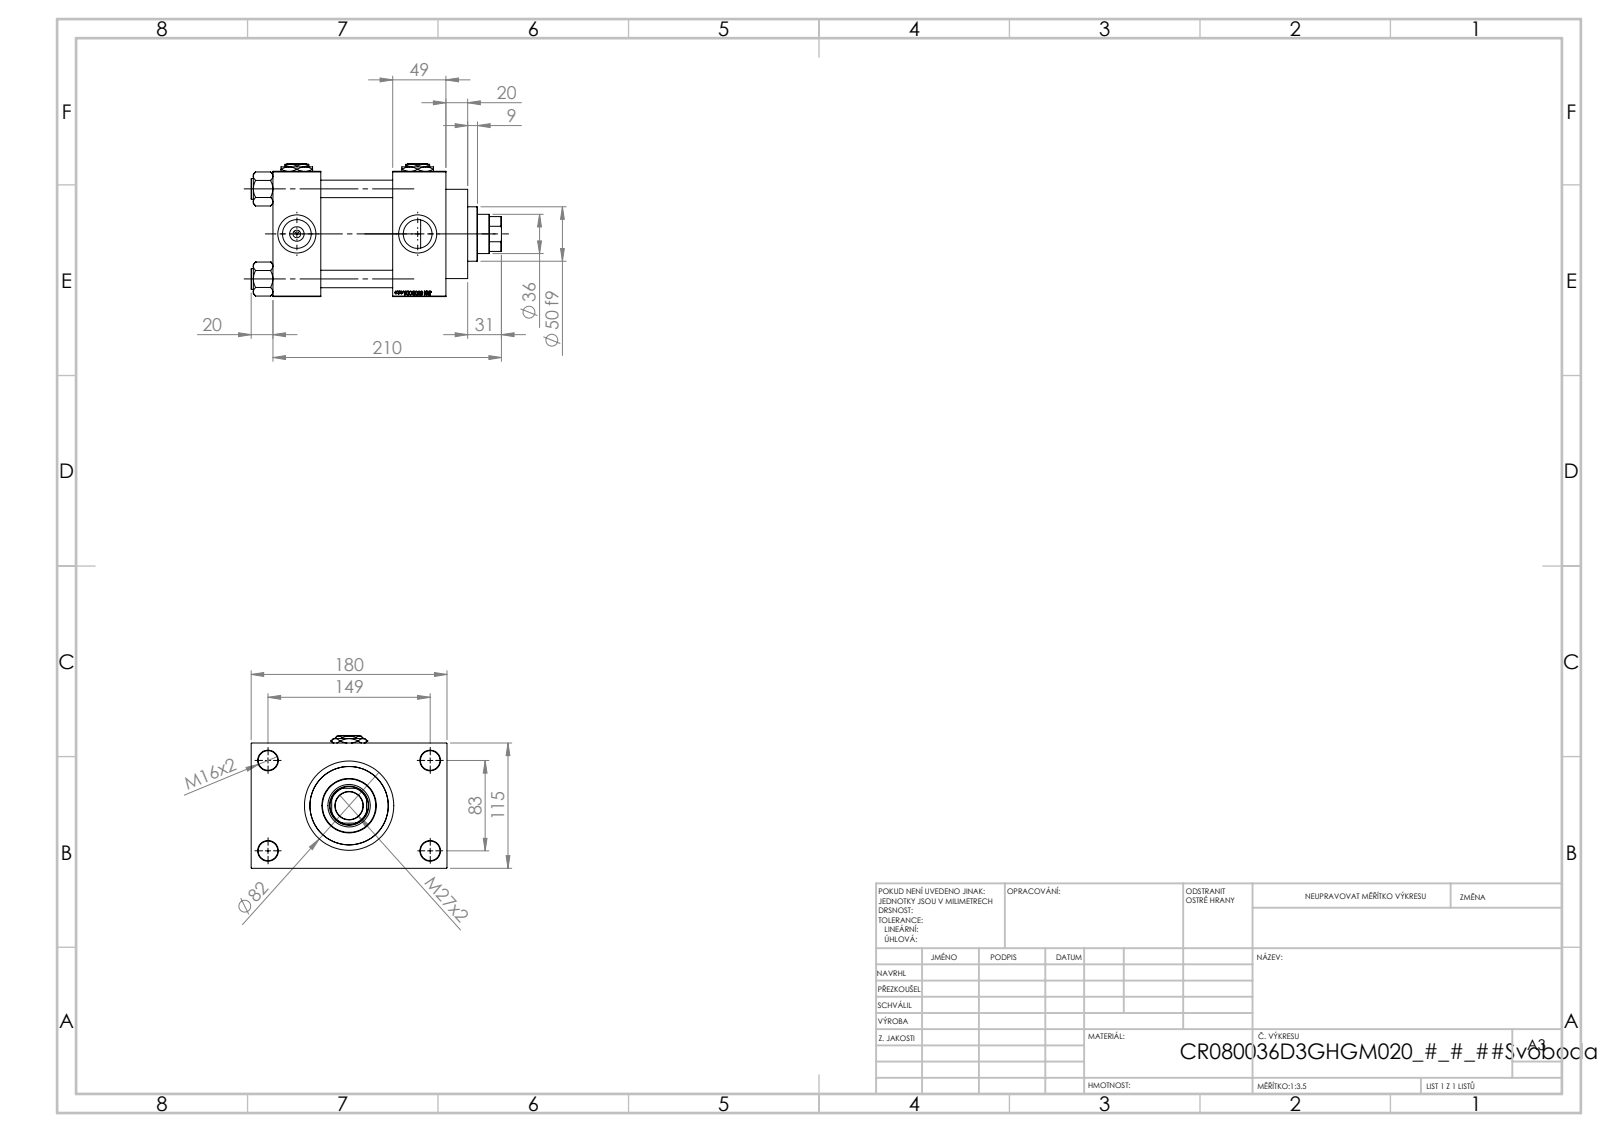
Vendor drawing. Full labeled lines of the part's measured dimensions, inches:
Part name (STEP PRODUCT): V215CR_VCP_D; NUT_M5_D; V215_VC_A; V215CR_D_Body (+2 more)
STEP written by: SolidWorks 2019 (CONFIG_CONTROL_DESIGN)
Units: inches
Bodies: 13 solids, 1252 faces (593 planar, 99 cylindrical, 560 other)
Overall size (bounding box): 9.055 × 7.087 × 4.803
Volume: 120 in³ · Surface area: 470.1 in²
Round holes (diameter × count): ⌀0.63 ×4, ⌀0.709 ×4, ⌀1.041 ×4, ⌀1.378 ×4, ⌀0.276 ×3, ⌀1.004 ×1, ⌀1.417 ×1, ⌀1.535 ×1, ⌀2.402 ×1, ⌀2.835 ×1, ⌀3.15 ×1
Round bosses / shafts (diameter × count): ⌀0.748 ×4, ⌀3.386 ×1, ⌀3.228 ×1, ⌀1.969 ×1
Partial cylindrical surfaces — rounded edges, fillets, slot ends (radius × count): R0.689 ×1
Main face-to-face distances: 4.528, 2.598, 4.331, 1.929, 1.732, 6.26, 1.28, 5.807, 0.787, 2.717
Hole centre spacings: 1.305, 2.302, 3.256, 3.357, 3.513, 4.561, 5.607, 3.268
